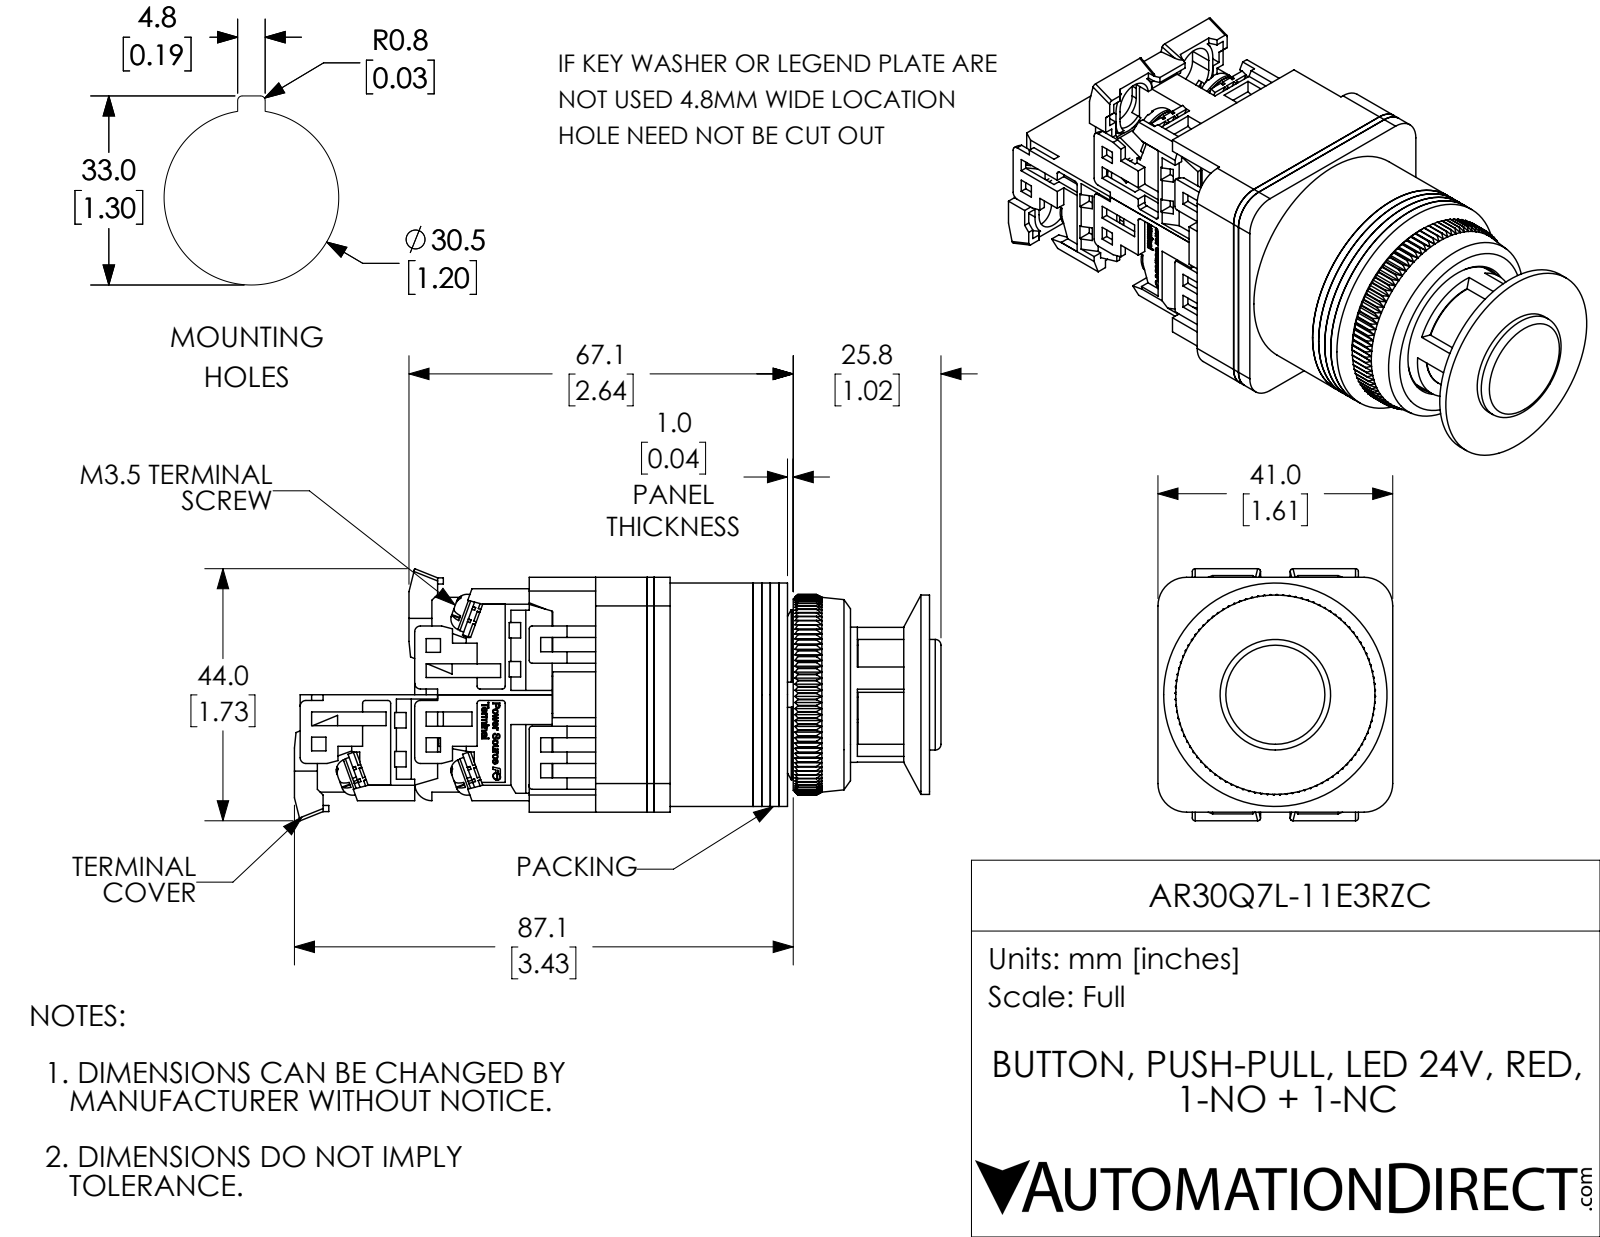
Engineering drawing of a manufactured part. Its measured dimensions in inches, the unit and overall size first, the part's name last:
Units: inches
Overall size (bounding box): 4.445 × 1.732 × 1.614
Round holes (diameter × count): ⌀0.138 ×8, ⌀0.142 ×6, ⌀0.217 ×1, ⌀0.335 ×1, ⌀0.453 ×1, ⌀0.571 ×1, ⌀0.669 ×1, ⌀0.681 ×1, ⌀0.76 ×1, ⌀0.768 ×1, ⌀0.945 ×1, ⌀0.965 ×1
Round bosses / shafts (diameter × count): ⌀0.26 ×6, ⌀0.138 ×6, ⌀1.535 ×1, ⌀1.37 ×1, ⌀1.181 ×1, ⌀1.087 ×1, ⌀0.929 ×1, ⌀0.827 ×1
Partial cylindrical surfaces — rounded edges, fillets, slot ends (radius × count): R0.059 ×24, R0.02 ×20, R0.039 ×6, R0.138 ×4, R0.177 ×4, R0.197 ×4, R0.118 ×3, R0.689 ×1
Main face-to-face distances: 0.059, 0.047, 0.118, 0.787, 0.858, 0.177, 0.807, 0.681, 0.063, 0.74
Hole centre spacings: 0.579, 0.638, 0.269, 0.269
Volume: 4.882 in³ · Surface area: 89.28 in²
Bodies: 34 solids, 2350 faces (1693 planar, 341 cylindrical, 316 other)
Part name (STEP PRODUCT): AR30Q7L-11E3RZC
STEP written by: SolidWorks 2017 (AUTOMOTIVE_DESIGN)
